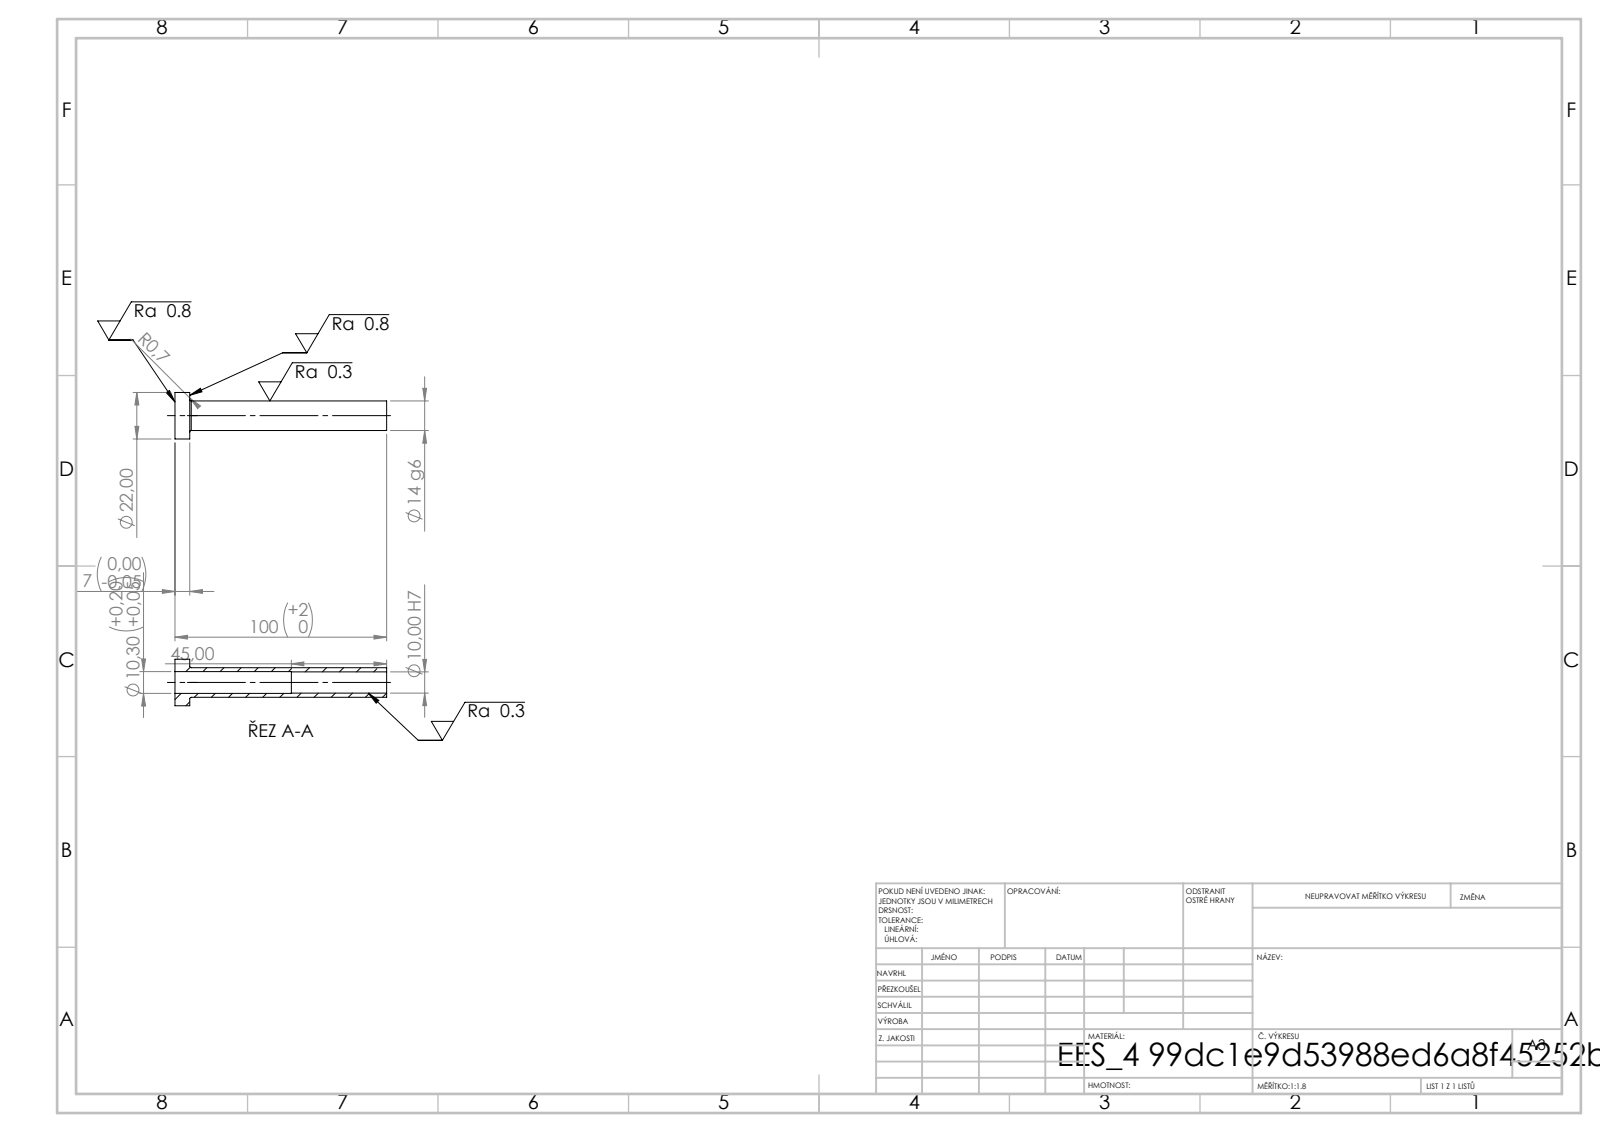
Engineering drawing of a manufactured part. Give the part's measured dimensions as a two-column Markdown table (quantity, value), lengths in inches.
| quantity | value |
| --- | --- |
| STEP written by | SolidWorks 2019 (CONFIG_CONTROL_DESIGN) |
| units | inches |
| bodies | 1 solid, 14 faces (4 planar, 8 cylindrical, 2 other) |
| overall size | 3.937 × 0.866 × 0.866 |
| volume | 0.541 in³ |
| surface area | 12.95 in² |
| round holes (diameter × count) | 0.394 × 1, 0.406 × 1 |
| round bosses / shafts (diameter × count) | 0.866 × 1, 0.551 × 1 |
| main face-to-face distances | 0.276, 3.937, 3.661, 2.165, 1.89, 1.772 |
